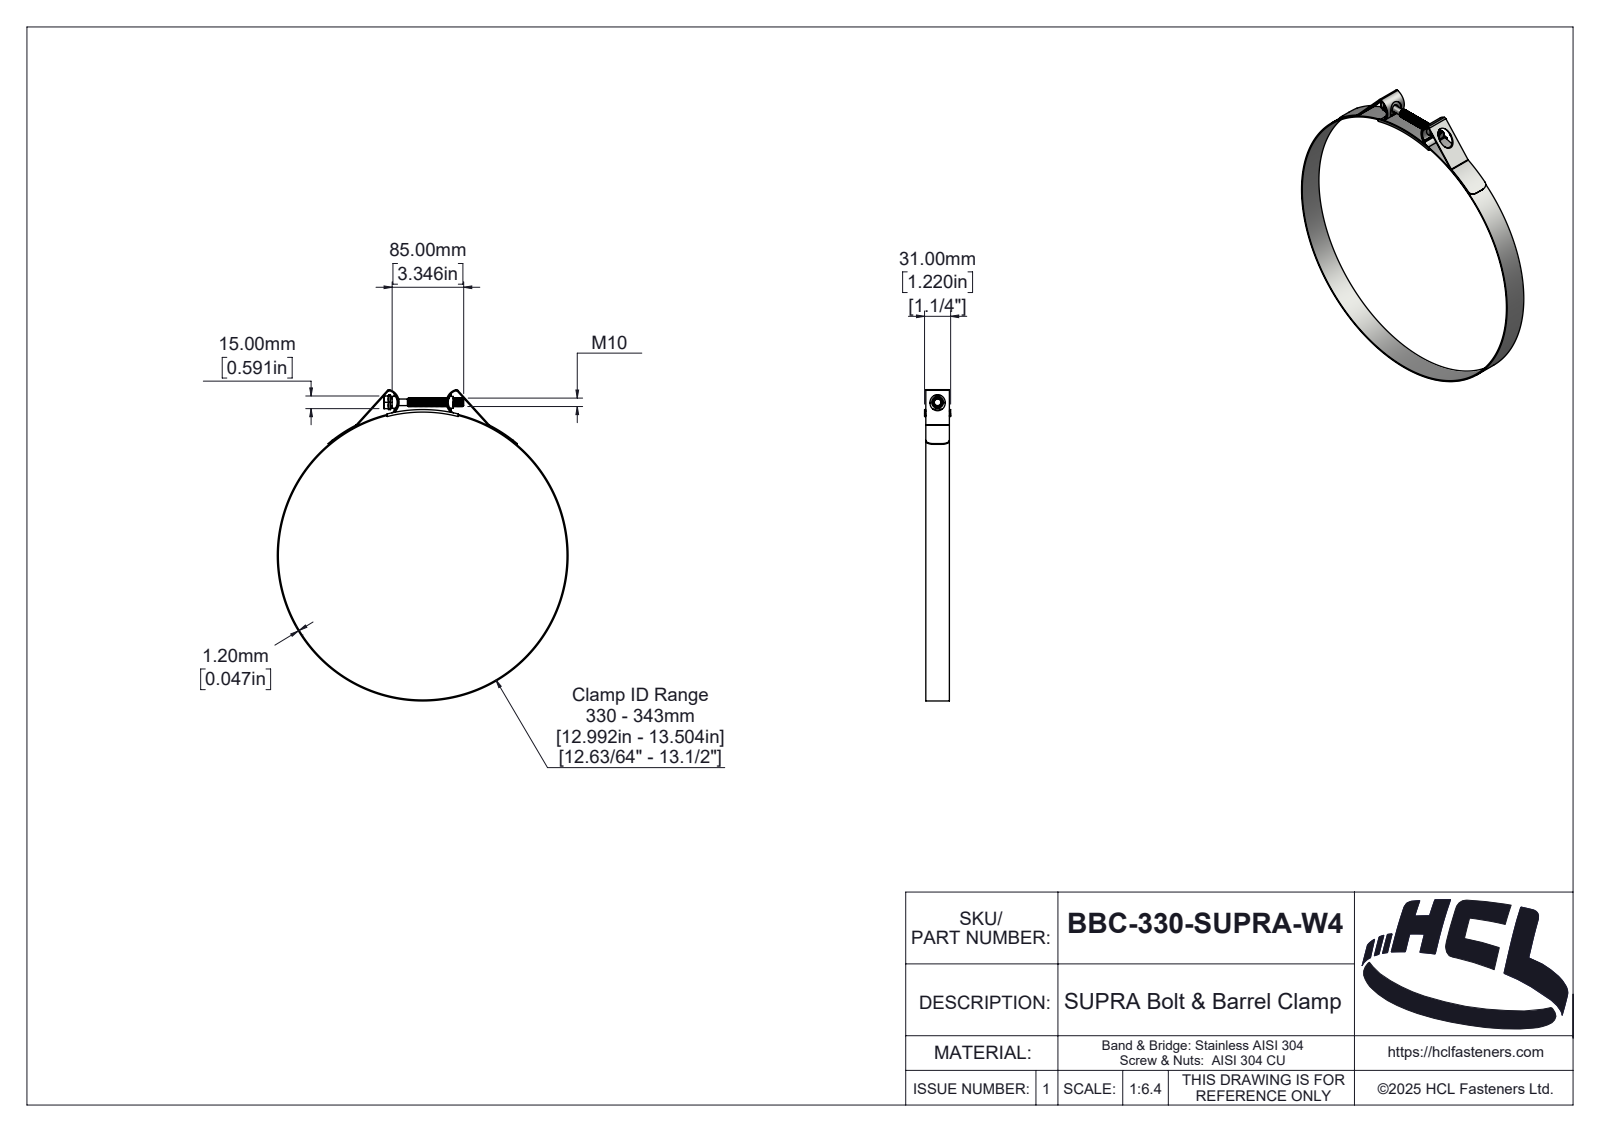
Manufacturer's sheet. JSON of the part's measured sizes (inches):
{"part_name": "BBC-330-SUPRA-W4", "step_written_by": "SolidWorks 2025 (AUTOMOTIVE_DESIGN)", "units": "inches", "bodies": {"solids": 5, "faces": 378, "planar": 50, "cylindrical": 242, "other": 86}, "overall_size": [14.552, 13.598, 1.22], "volume_in3": 3.301, "surface_area_in2": 133.3, "round_holes": [[13.504, 1]], "round_bosses_or_shafts": [[13.598, 1], [0.682, 1], [0.551, 1], [0.394, 1], [0.307, 1]], "partial_cylinders_radius": [[0.039, 4], [0.051, 2], [0.079, 2], [0.098, 2], [0.126, 2], [0.354, 2], [0.522, 2], [0.561, 2]], "face_to_face_distances": [0.047, 1.102, 0.059, 1.161, 1.173, 1.114, 1.22, 1.126, 0.591, 0.098]}
